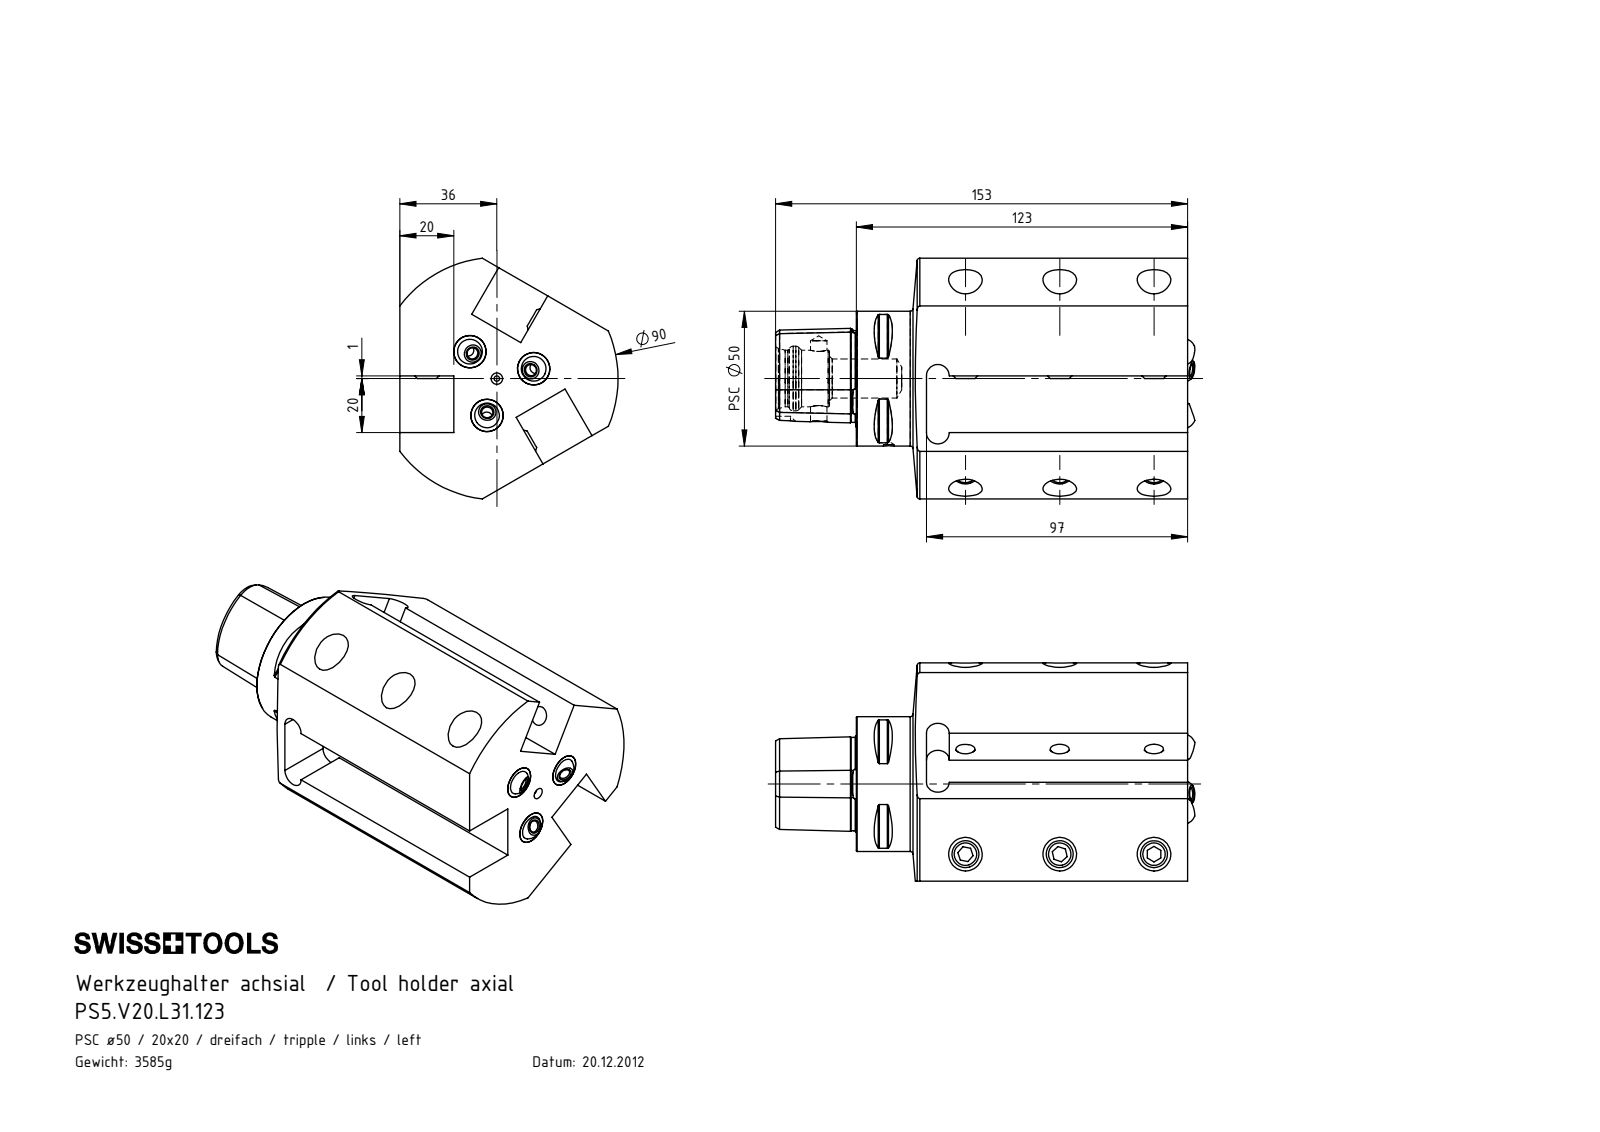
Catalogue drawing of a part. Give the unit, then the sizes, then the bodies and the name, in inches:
Units: inches
Overall size (bounding box): 6.094 × 3.518 × 3.189
Round holes (diameter × count): ⌀0.335 ×10, ⌀0.492 ×9, ⌀0.165 ×6, ⌀0.276 ×3, ⌀0.472 ×3, ⌀0.079 ×1, ⌀0.157 ×1, ⌀0.24 ×1, ⌀0.571 ×1, ⌀0.827 ×1, ⌀0.945 ×1
Round bosses / shafts (diameter × count): ⌀0.394 ×9, ⌀1.969 ×1
Partial cylindrical surfaces — rounded edges, fillets, slot ends (radius × count): R0.02 ×8, R0.167 ×6, R0.157 ×1, R1.772 ×1
Main face-to-face distances: 0.787, 0.827, 3.819, 4.843, 1.024, 4.528, 3.504, 0.315, 0.197, 1.181
Hole centre spacings: 1.378, 0.557, 0.964, 2.756, 1.024, 1.519, 2.377, 2.702
Volume: 27.91 in³ · Surface area: 130.8 in²
Bodies: 16 solids, 294 faces (127 planar, 70 cylindrical, 97 other)
Part name (STEP PRODUCT): ISO 4026 - M10 x 25; PS5.V20.L31.123; KU1-U12.001.010_2; KU1-U12.001.010 (+2 more)
STEP written by: SolidWorks 2017 (AUTOMOTIVE_DESIGN)
